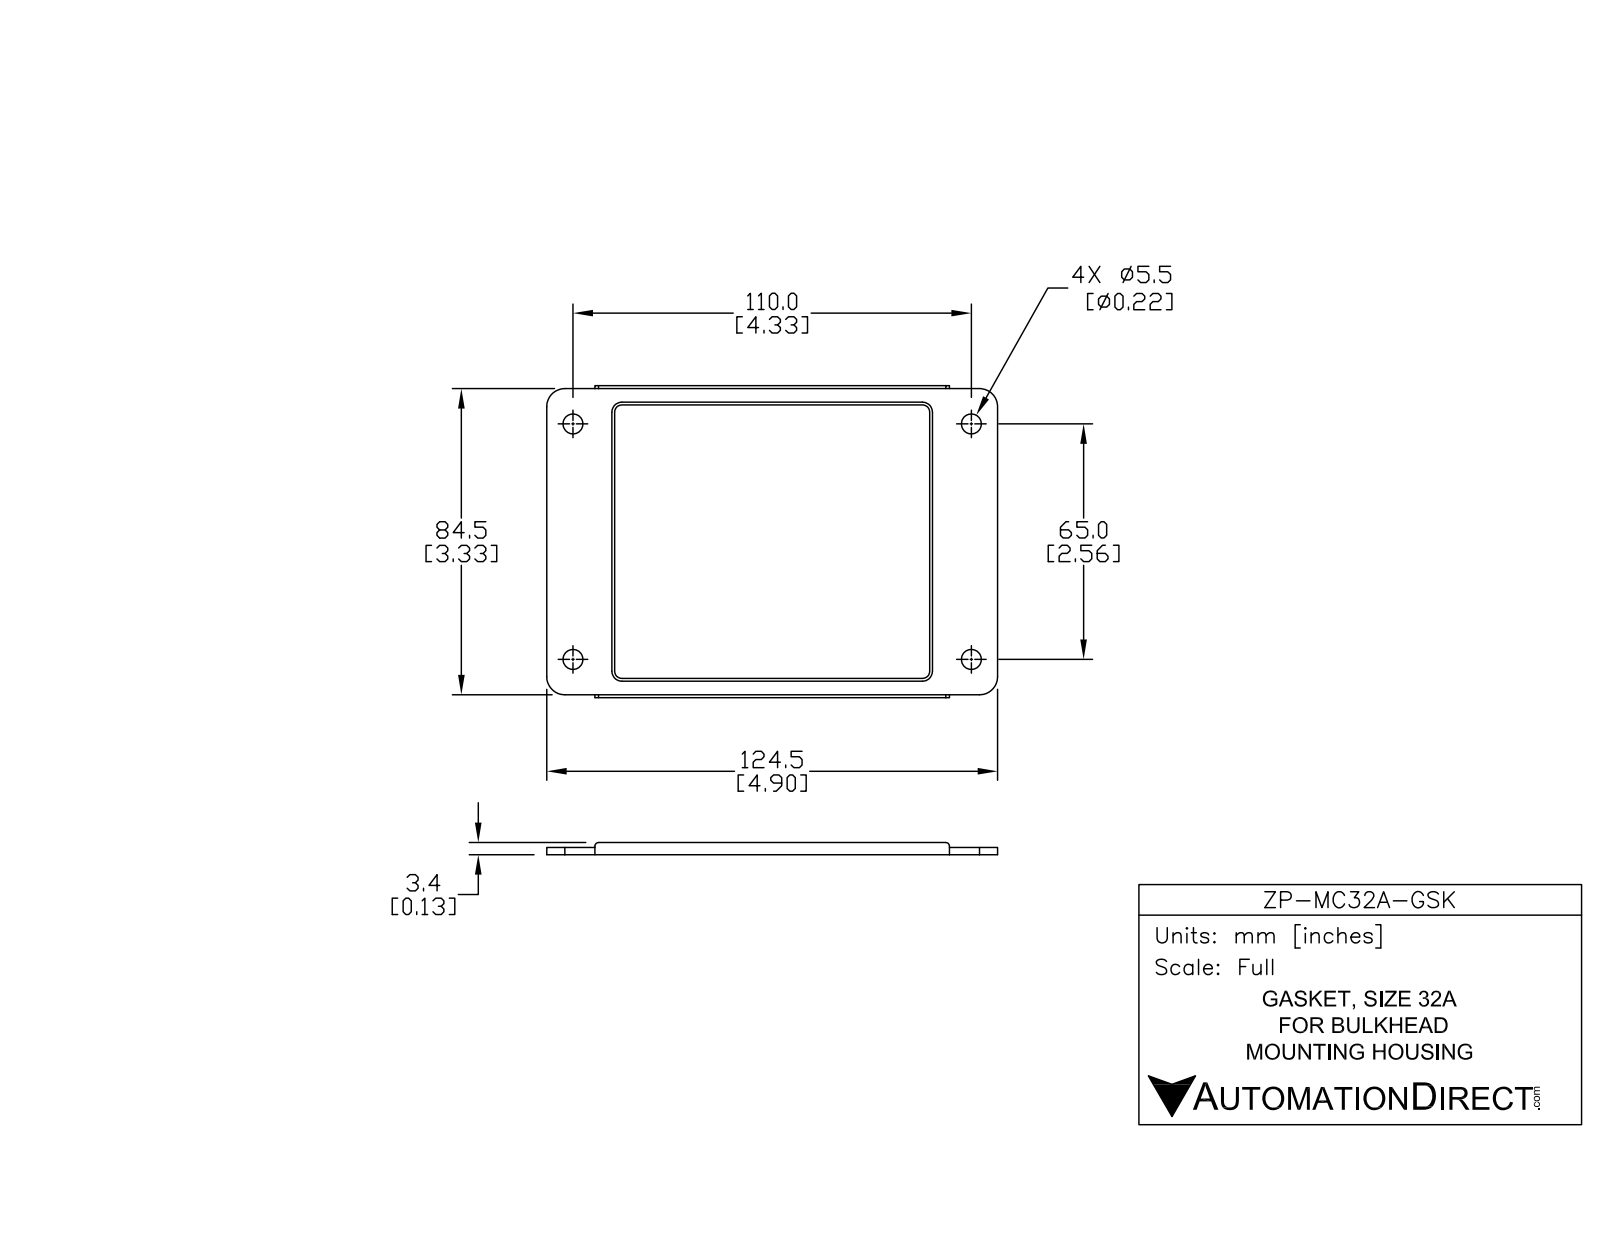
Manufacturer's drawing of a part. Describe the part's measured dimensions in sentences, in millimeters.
The part is named "ZP-MC32B-GSK". Its 3-D file was written by "SolidWorks 2014 (AUTOMOTIVE_DESIGN)". It is 1 solid with 51 faces: 27 planar, 24 cylindrical and 0 other. Overall it measures 124.5 by 86.1 by 3.35 millimeters. Its volume is 8 529 cubic millimeters and its surface area 11 002 square millimeters. Round holes: 4 of diameter 5.5. Partial cylindrical surfaces (rounded edges, fillets, slot ends): 4 of radius 2, 4 of radius 2.75, 4 of radius 5, 2 of radius 1. The main face-to-face distances are 2, 5.3, 80.8, 0.75, 3.35, 1.35, 0.8, 85.3, 4.5, 80. The hole center spacings are 65, 110, 127.77.
